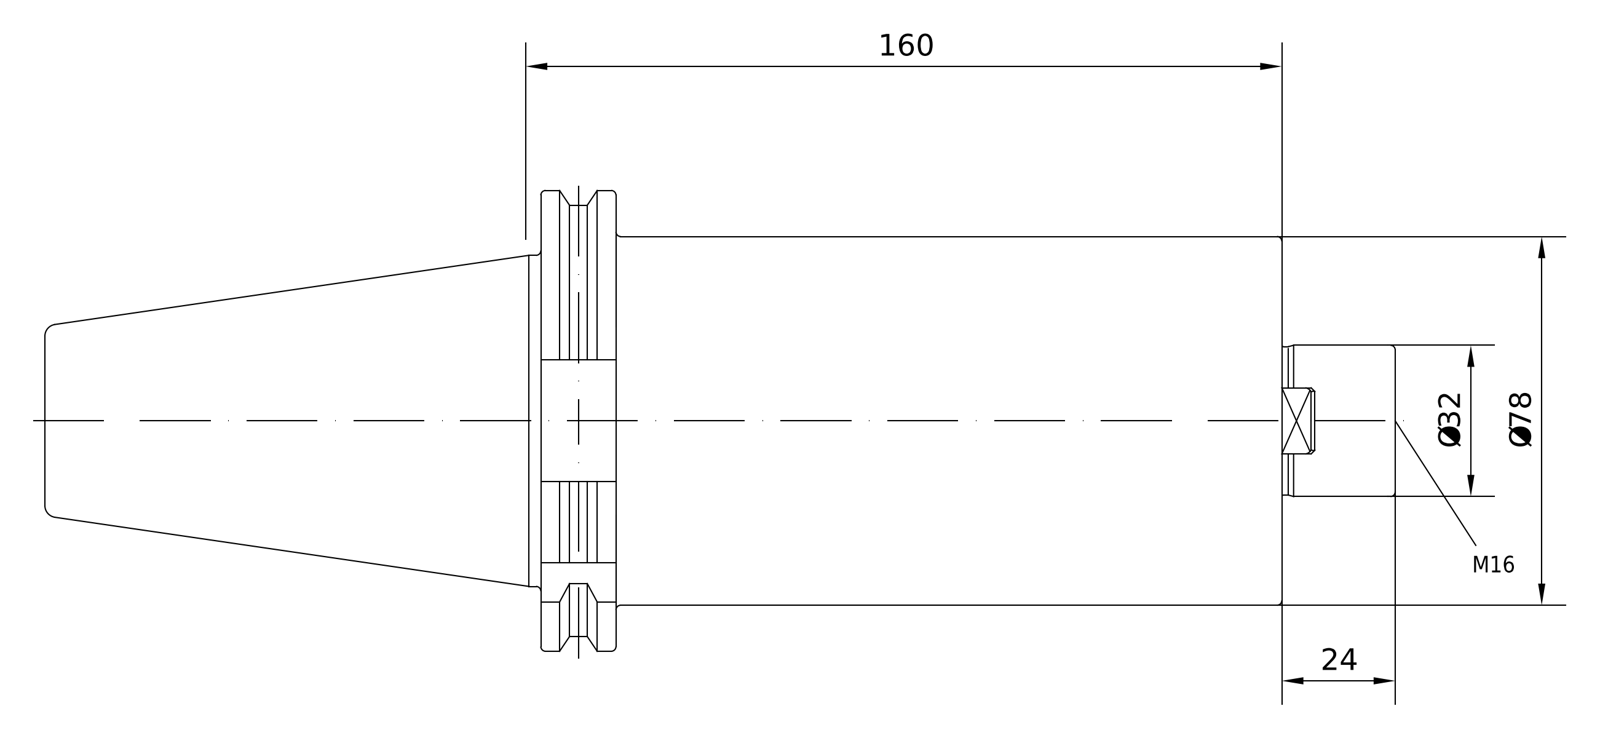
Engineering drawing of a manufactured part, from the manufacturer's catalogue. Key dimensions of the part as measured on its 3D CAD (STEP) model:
Part name (STEP PRODUCT): 50-352-32
STEP written by: PRO/ENGINEER BY PARAMETRIC TECHNOLOGY CORPORATION, 2010430 (CONFIG_CONTROL_DESIGN)
Units: millimetres
Bodies: 1 solid, 112 faces (35 planar, 28 cylindrical, 49 other)
Overall size (bounding box): 285.6 × 97.47 × 94
Volume: 1 027 000 mm³ · Surface area: 83 721 mm²
Round holes (diameter × count): ⌀14 ×1, ⌀16 ×1, ⌀20.75 ×1, ⌀25.01 ×1, ⌀25.7 ×1
Round bosses / shafts (diameter × count): ⌀91 ×1, ⌀78 ×1, ⌀69.15 ×1, ⌀32 ×1, ⌀24.01 ×1
Partial cylindrical surfaces — rounded edges, fillets, slot ends (radius × count): R1.75 ×1, R48.74 ×1
Main face-to-face distances: 156.8, 15.85, 140.95, 72.8, 180.8, 164.95, 24, 163.8, 147.95, 7
